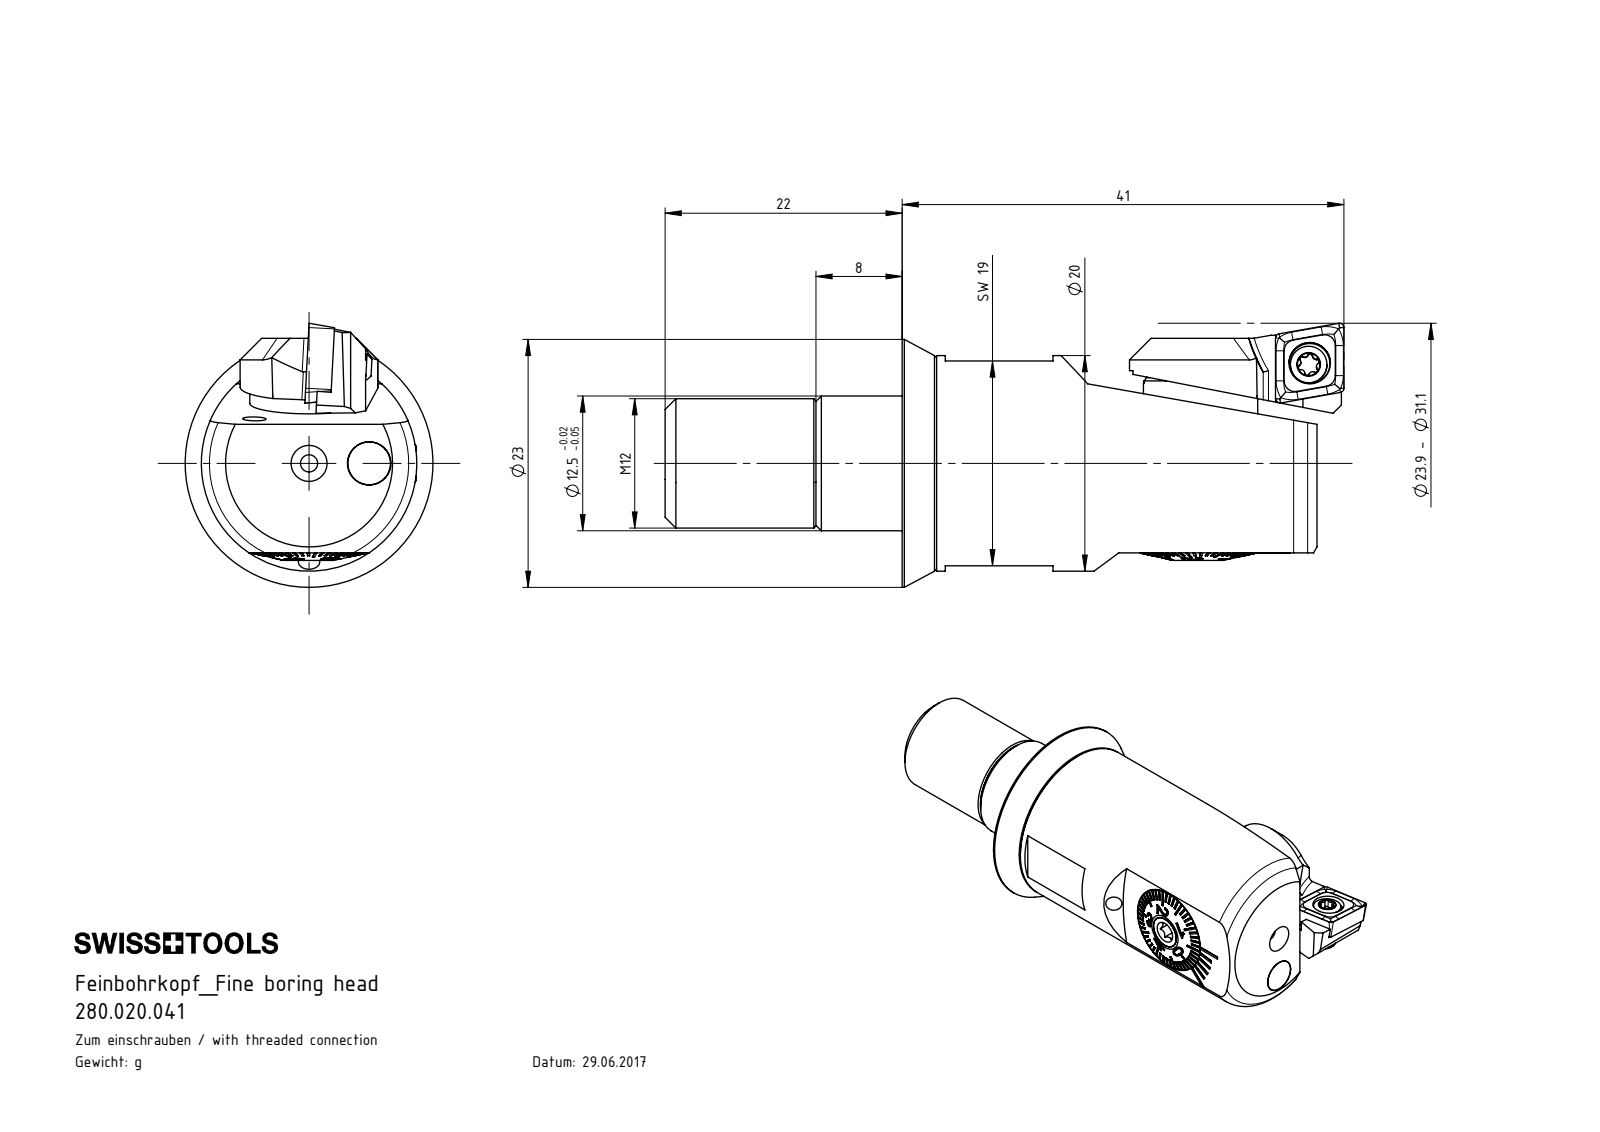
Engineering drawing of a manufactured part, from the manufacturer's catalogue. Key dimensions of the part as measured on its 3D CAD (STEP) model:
Part name (STEP PRODUCT): F20-BG1.008.006_A; Klebstoff D4; DIN 3771 - 11x1_x; HP4-ER2.008.028_A (+8 more)
STEP written by: SolidWorks 2017 (CONFIG_CONTROL_DESIGN)
Units: millimetres
Bodies: 17 solids, 787 faces (338 planar, 148 cylindrical, 301 other)
Overall size (bounding box): 63 × 23.35 × 23
Volume: 13 060 mm³ · Surface area: 10 102 mm²
Round holes (diameter × count): ⌀2 ×4, ⌀3.3 ×3, ⌀1.6 ×1, ⌀1.9 ×1, ⌀2.05 ×1, ⌀2.5 ×1, ⌀2.8 ×1, ⌀3 ×1, ⌀3.85 ×1, ⌀4 ×1, ⌀4.5 ×1, ⌀5.4 ×1
Round bosses / shafts (diameter × count): ⌀4 ×2, ⌀3.95 ×2, ⌀23 ×1, ⌀20 ×1, ⌀12 ×1, ⌀10.98 ×1, ⌀10.85 ×1, ⌀8.65 ×1
Partial cylindrical surfaces — rounded edges, fillets, slot ends (radius × count): R0.21 ×6, R0.36 ×5, R0.3 ×2, R0.5 ×2, R2 ×2, R3 ×2, R5 ×2, R0.36 ×1
Main face-to-face distances: 3, 6, 38.5, 35.5, 15.1, 11.35, 3.75, 8, 11, 46.5
Hole centre spacings: 5.6, 7, 12.6, 14
